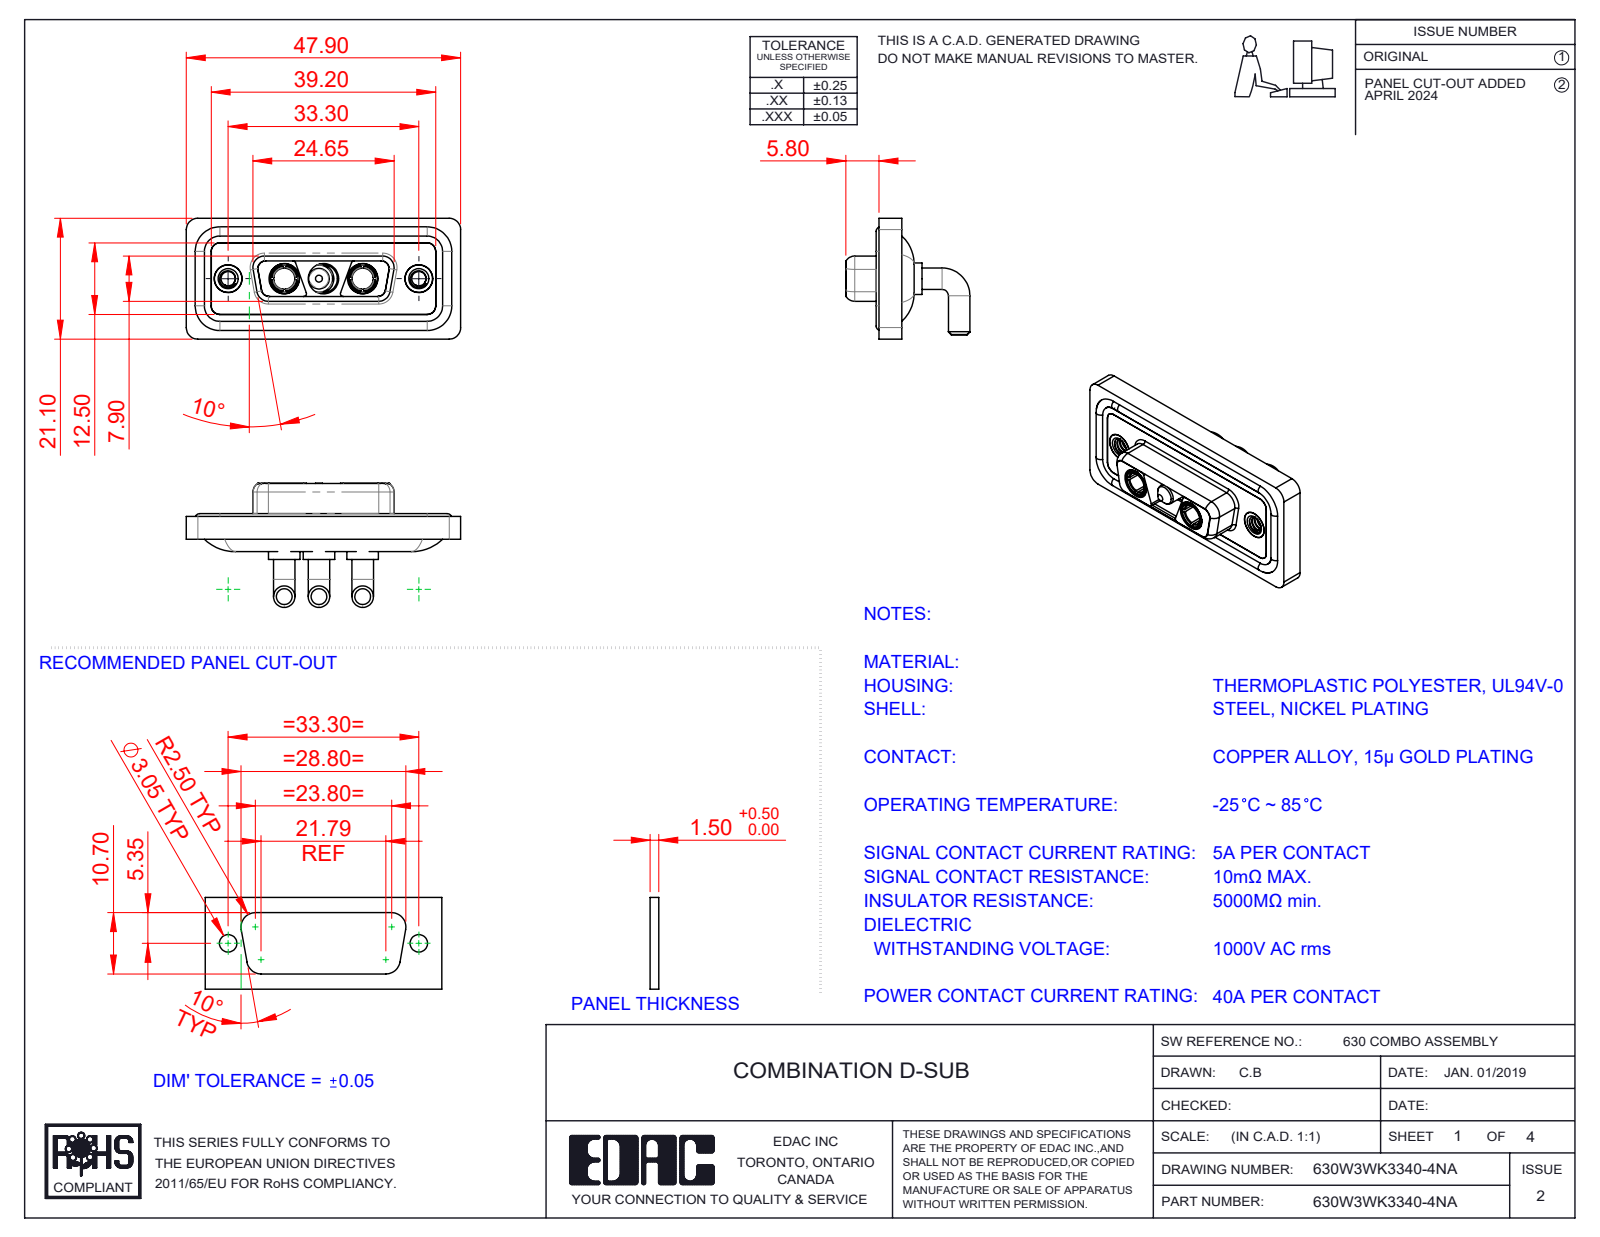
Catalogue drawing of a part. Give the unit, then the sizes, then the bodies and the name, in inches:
Units: inches
Overall size (bounding box): 1.886 × 0.854 × 0.831
Round holes (diameter × count): ⌀0.191 ×5, ⌀0.209 ×3, ⌀0.098 ×2, ⌀0.146 ×2, ⌀0.157 ×2, ⌀0.159 ×2, ⌀0.197 ×2
Round bosses / shafts (diameter × count): ⌀0.148 ×6, ⌀0.063 ×4, ⌀0.217 ×3, ⌀0.205 ×3, ⌀0.187 ×3, ⌀0.195 ×2, ⌀0.195 ×2, ⌀0.189 ×2
Partial cylindrical surfaces — rounded edges, fillets, slot ends (radius × count): R0.079 ×20, R0.059 ×18, R0.053 ×12, R0.02 ×8, R0.063 ×8, R0.01 ×4, R0.024 ×4, R0.026 ×4
Main face-to-face distances: 0.016, 0.071, 0.043, 0.063, 0.114, 0.098, 0.122, 0.146, 0.161, 0.059
Hole centre spacings: 0.27, 0.386, 0.656, 0.925, 0.539, 1.311
Volume: 0.381 in³ · Surface area: 15.3 in²
Bodies: 13 solids, 589 faces (178 planar, 262 cylindrical, 149 other)
Part name (STEP PRODUCT): 630W3WK3340-4NA; 630Combo Waterproof Housing_15 Contacts; 630Combo Housing_3WK3; 630Combo Shell Front_15 Contacts (+4 more)
STEP written by: SolidWorks 2023 (CONFIG_CONTROL_DESIGN)
